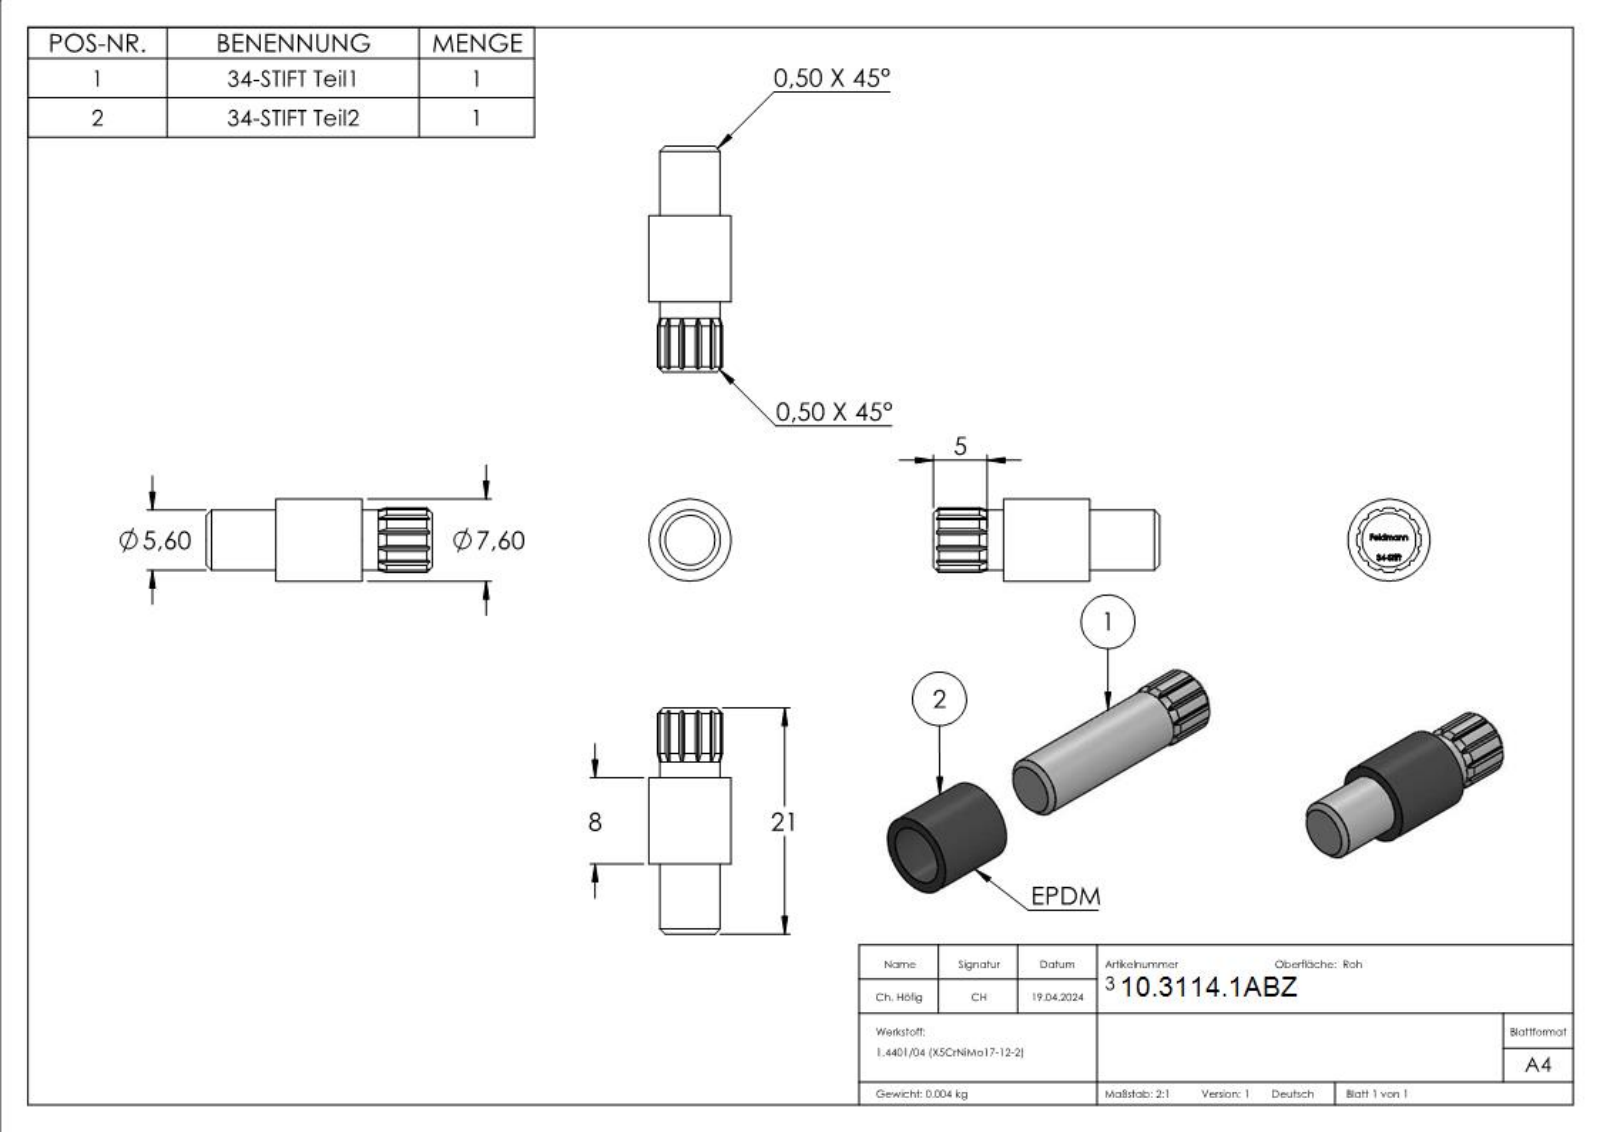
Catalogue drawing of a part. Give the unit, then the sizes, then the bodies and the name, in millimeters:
Units: millimetres
Overall size (bounding box): 21 × 7.6 × 7.6
Round holes (diameter × count): ⌀5.6 ×1
Round bosses / shafts (diameter × count): ⌀7.6 ×1
Partial cylindrical surfaces — rounded edges, fillets, slot ends (radius × count): R3 ×1
Main face-to-face distances: 6.5, 14.5, 8, 21, 4.03, 4.04, 6.4, 14.4, 20.9, 0.63
Volume: 692 mm³ · Surface area: 801 mm²
Bodies: 2 solids, 286 faces (165 planar, 19 cylindrical, 102 other)
Part name (STEP PRODUCT): 34-Stift Teil1; 34-Stift; 34-Stift Teil2
STEP written by: SolidWorks 2015 (CONFIG_CONTROL_DESIGN)
